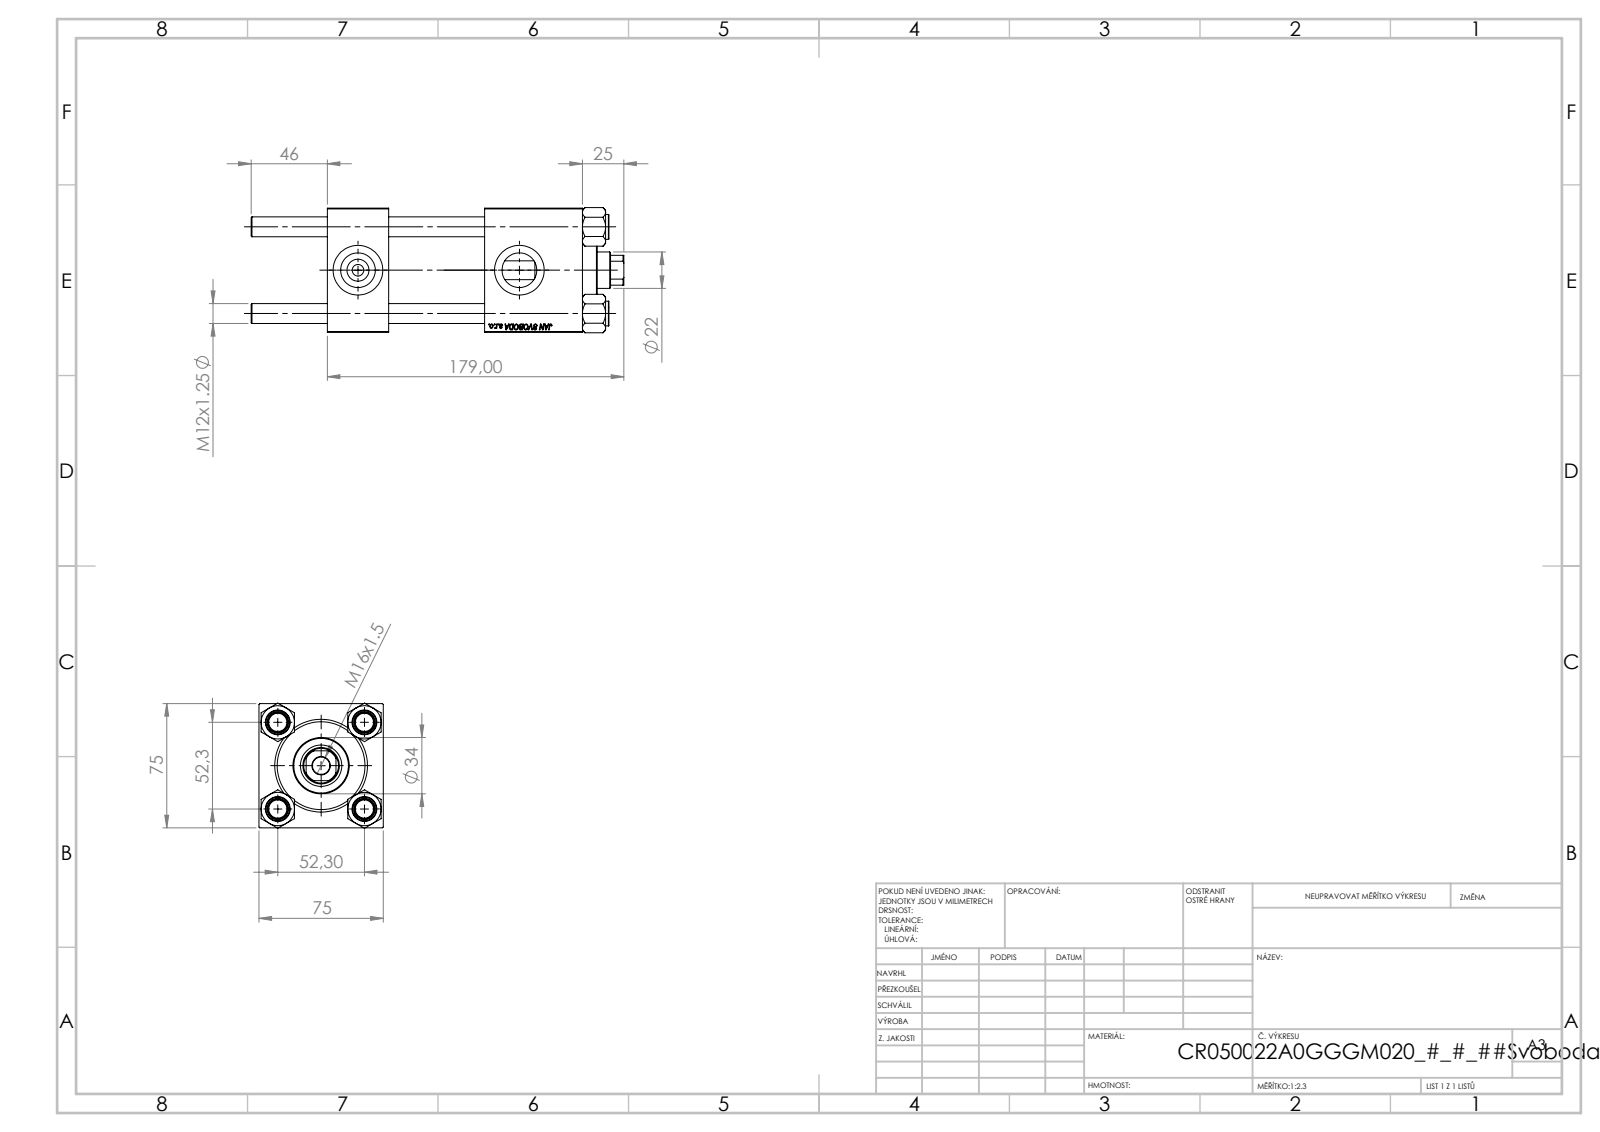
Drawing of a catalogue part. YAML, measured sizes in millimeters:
part_name: "V215CR_BODY_A; NUT_M5; V215CR_VCP; V215_VC_A (+1 more)"
step_written_by: "SolidWorks 2019 (CONFIG_CONTROL_DESIGN)"
units: millimeters
bodies: {solids: 11, faces: 1135, planar: 520, cylindrical: 79, other: 536}
overall_size: [225, 75.54, 75]
volume: 689092
surface_area: 163505
round_holes:
  - {diameter: 12, count: 4}
  - {diameter: 7, count: 2}
  - {diameter: 20.96, count: 2}
  - {diameter: 30, count: 2}
  - {diameter: 10.5, count: 1}
  - {diameter: 22, count: 1}
  - {diameter: 25, count: 1}
  - {diameter: 41, count: 1}
  - {diameter: 50, count: 1}
  - {diameter: 53, count: 1}
round_bosses_or_shafts:
  - {diameter: 15, count: 4}
  - {diameter: 56, count: 1}
  - {diameter: 34, count: 1}
partial_cylinders:
  - {radius: 10.5, count: 1}
face_to_face_distances: [75, 37, 154, 117, 95, 59, 58, 28.7, 125.3, 88.3]
hole_center_spacings: [36.98, 52.3, 73.96, 97.46]
